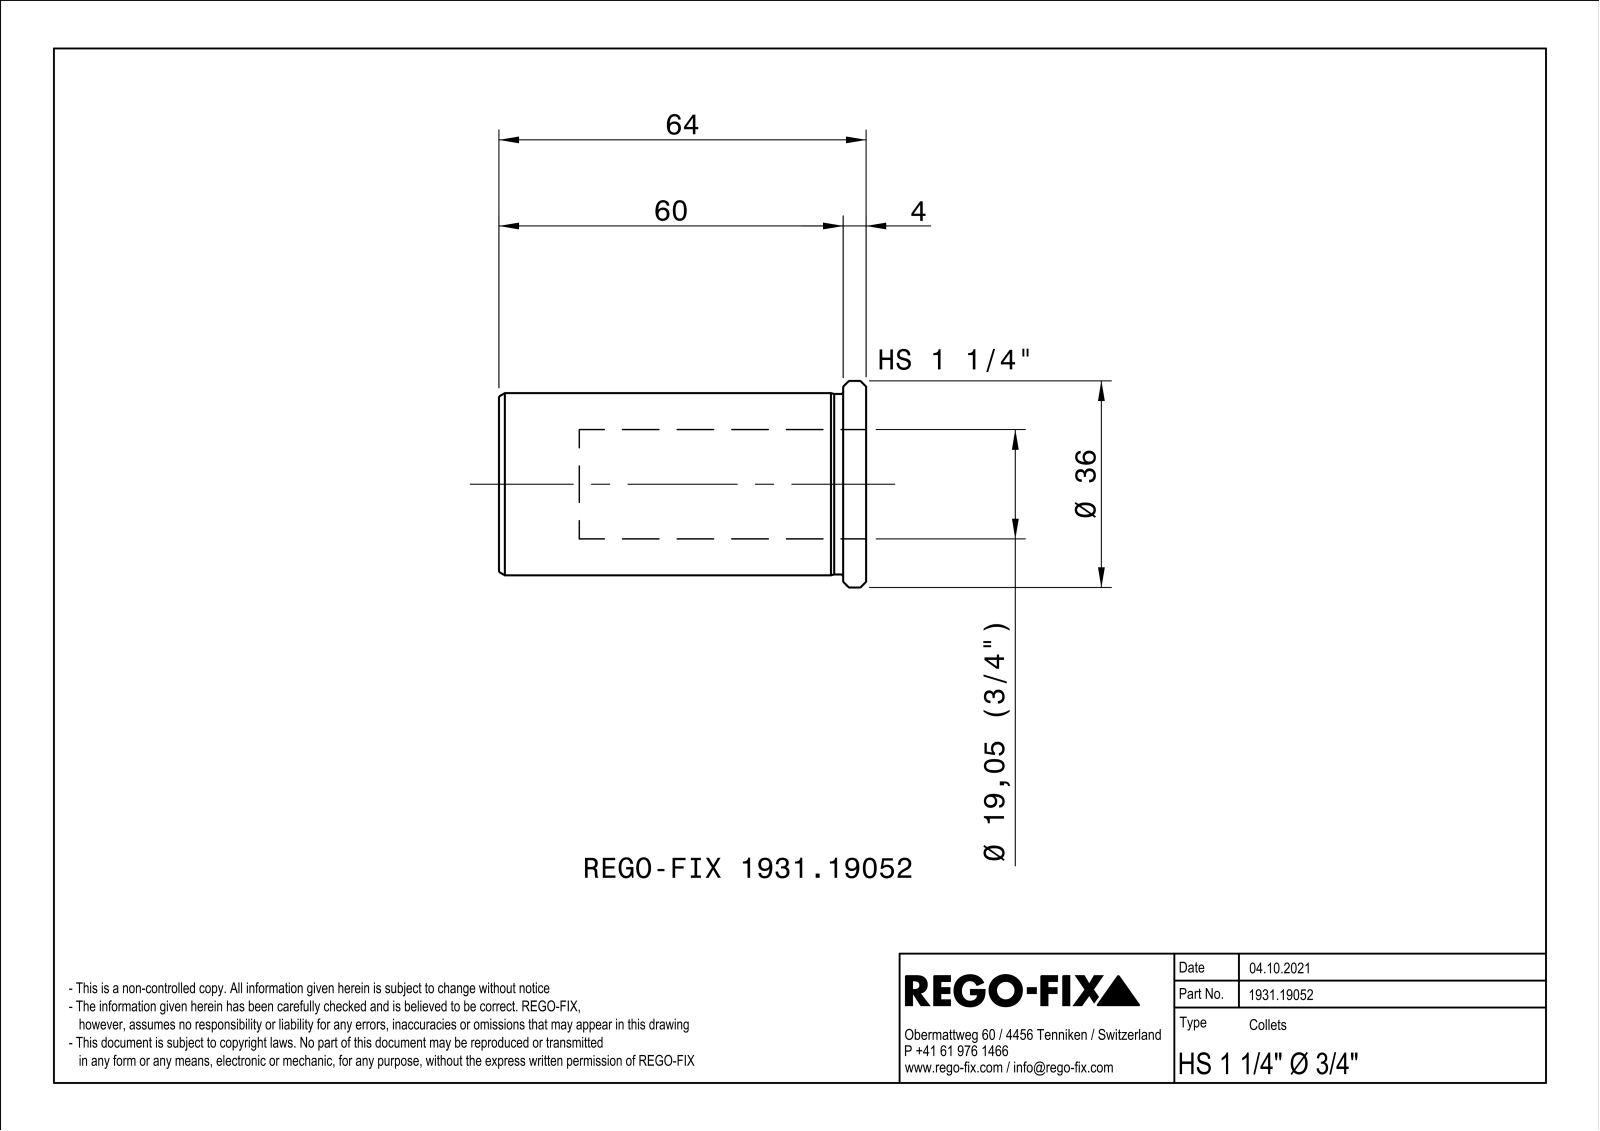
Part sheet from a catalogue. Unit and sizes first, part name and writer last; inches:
Units: inches
Overall size (bounding box): 2.52 × 1.417 × 1.417
Round holes (diameter × count): ⌀0.75 ×1, ⌀1.043 ×1
Round bosses / shafts (diameter × count): ⌀1.417 ×1, ⌀1.25 ×1, ⌀1.238 ×1
Main face-to-face distances: 0.039, 2.52, 0.157, 2.362
Volume: 1.749 in³ · Surface area: 21 in²
Bodies: 1 solid, 70 faces (22 planar, 11 cylindrical, 37 other)
Part name (STEP PRODUCT): NOCUT
STEP written by: SIEMENS PLM Software Solid Edge ST10 (AUTOMOTIVE_DESIGN)
